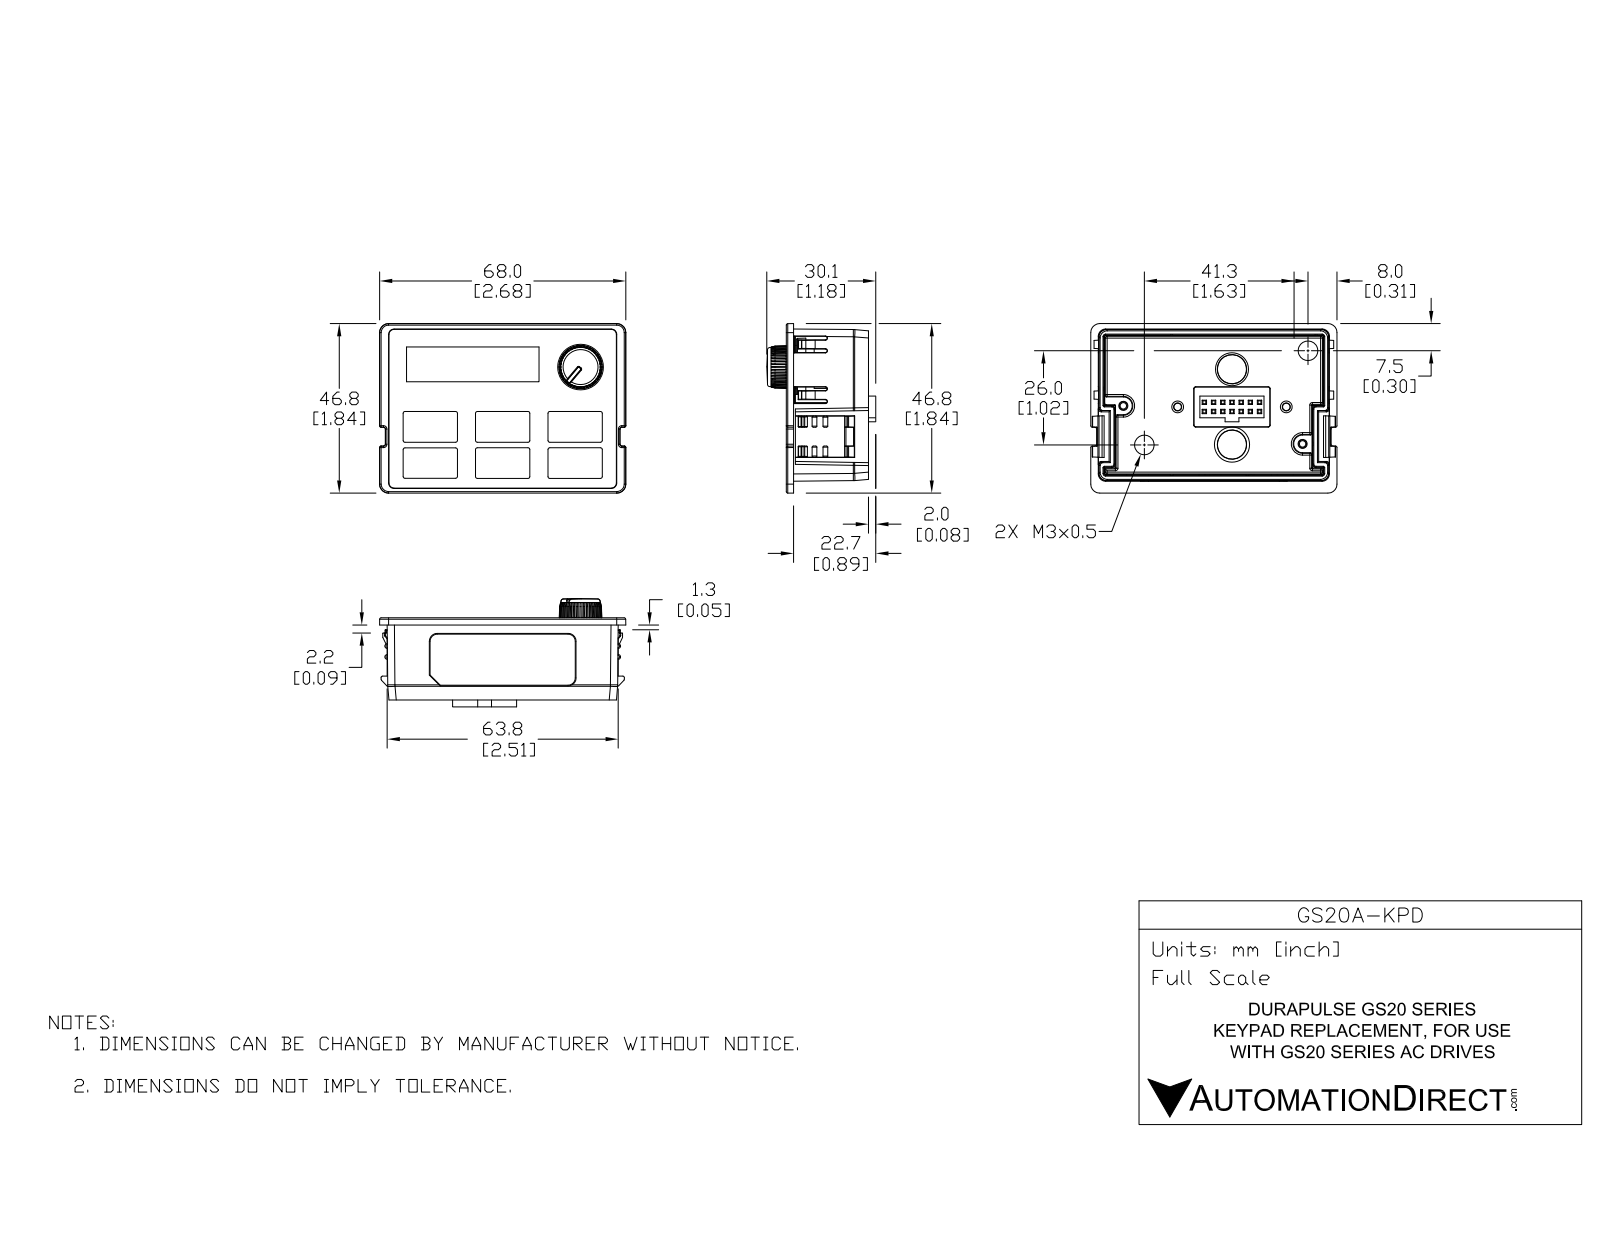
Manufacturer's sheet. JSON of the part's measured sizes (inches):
{"part_name": "KPMS-LE01-PD-3D00 with NEW KNOB R1", "step_written_by": "SolidWorks 2017 (AUTOMOTIVE_DESIGN)", "units": "inches", "bodies": {"solids": 8, "faces": 1195, "planar": 606, "cylindrical": 334, "other": 255}, "overall_size": [2.677, 1.843, 1.176], "volume_in3": 1.015, "surface_area_in2": 42.08, "round_holes": [[0.181, 2], [0.429, 1], [0.496, 1]], "round_bosses_or_shafts": [[0.025, 10], [0.169, 2], [0.102, 2]], "partial_cylinders_radius": [[0.008, 53], [0.02, 43], [0.016, 20], [0.079, 11], [0.004, 10], [0.031, 8], [0.059, 8], [0.026, 4]], "face_to_face_distances": [0.87, 0.862, 1.583, 0.071, 0.791, 0.799, 0.02, 0.118, 2.328, 0.067], "hole_center_spacings": [0.851, 0.856, 1.874, 1.878, 2.053]}
